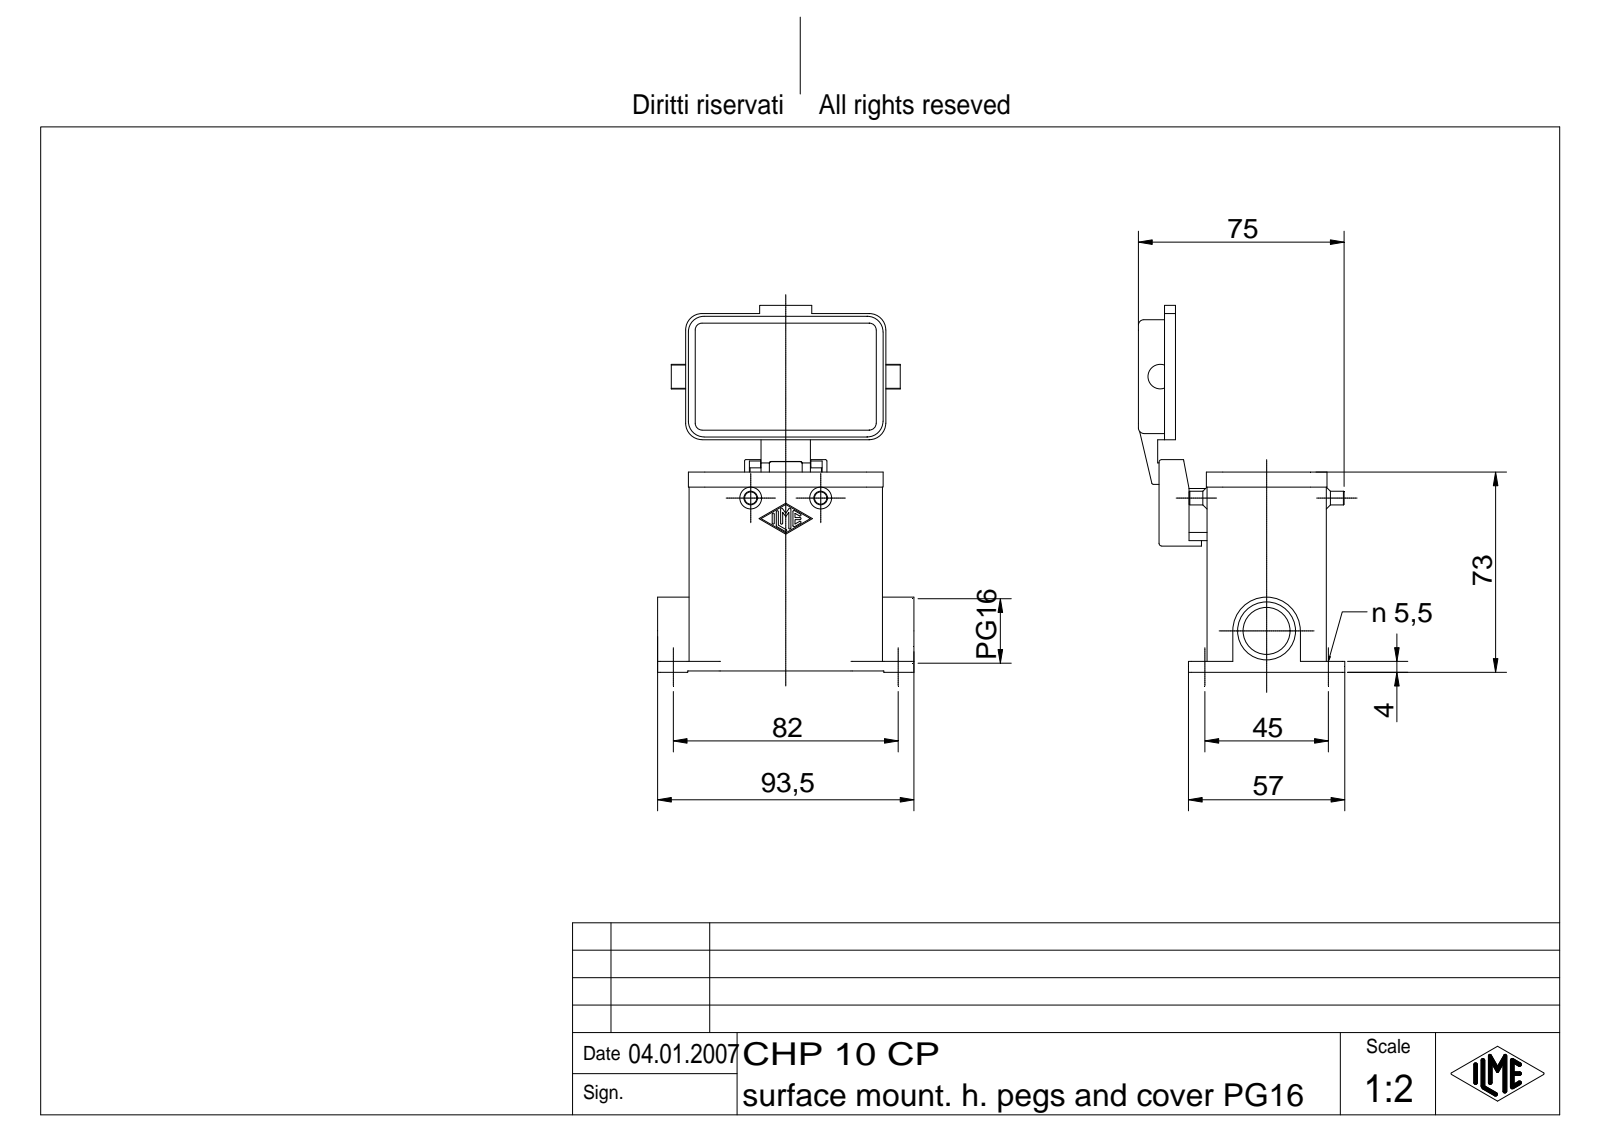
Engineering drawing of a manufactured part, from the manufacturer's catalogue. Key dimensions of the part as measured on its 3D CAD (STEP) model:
Part name (STEP PRODUCT): CHP 10 CP
STEP written by: Autodesk Inventor 7 (AUTOMOTIVE_DESIGN)
Units: millimetres
Bodies: 1 solid, 470 faces (195 planar, 164 cylindrical, 111 other)
Overall size (bounding box): 133.75 × 93.5 × 75.25
Volume: 109 146 mm³ · Surface area: 60 050 mm²
Round holes (diameter × count): ⌀5.5 ×4, ⌀4 ×1, ⌀5 ×1, ⌀17.16 ×1, ⌀21.16 ×1
Round bosses / shafts (diameter × count): ⌀5 ×2, ⌀3 ×2, ⌀7 ×1, ⌀4 ×1
Partial cylindrical surfaces — rounded edges, fillets, slot ends (radius × count): R0.38 ×14, R1 ×14, R6 ×12, R0.5 ×10, R0.7 ×8, R2 ×8, R2.5 ×4, R3 ×4
Main face-to-face distances: 3, 40.5, 43.5, 2.5, 68.5, 37.5, 22.5, 66, 63, 3.5
Hole centre spacings: 45, 82, 93.54
